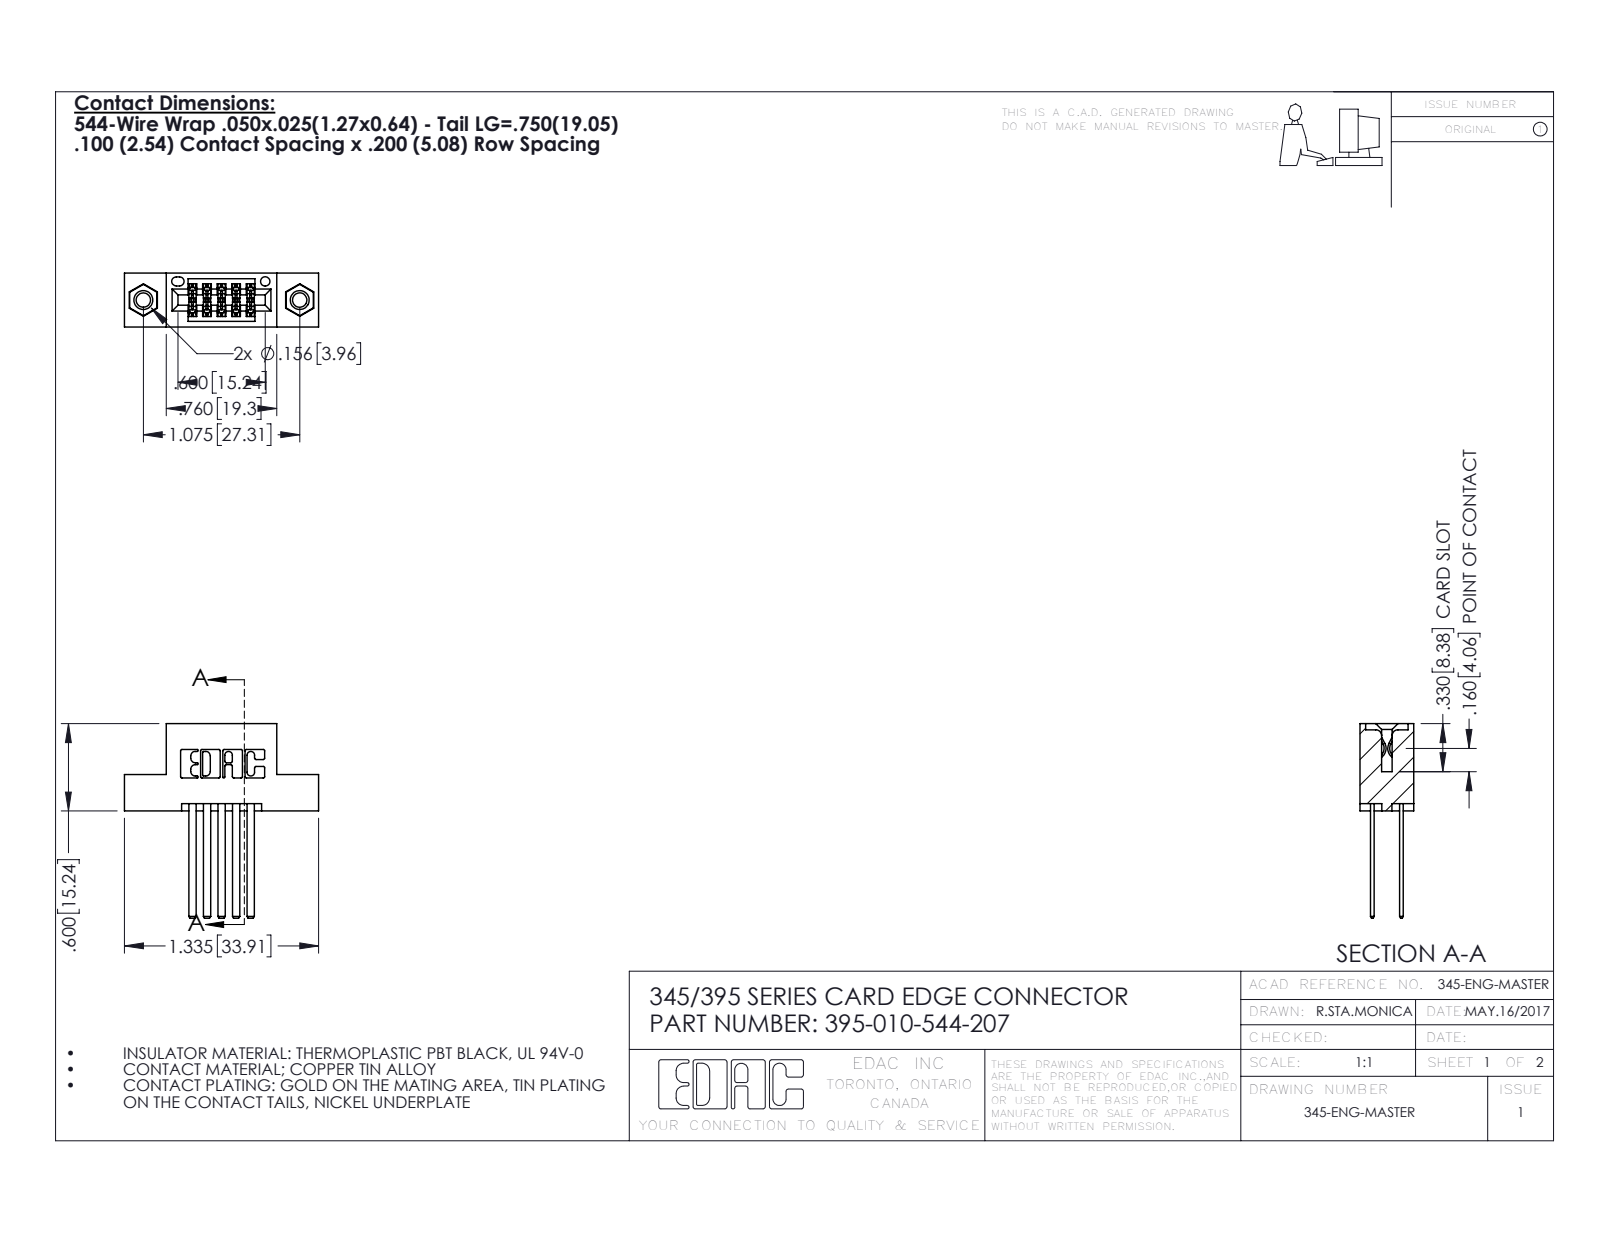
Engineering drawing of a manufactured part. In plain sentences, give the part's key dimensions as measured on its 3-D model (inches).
The part is named "345-250-001_345-250-005-103; 345-292-001_345-293-144; 395-010-544-207; 345 Part_Flush Mounting Lugs - 0.156 Dia-TI". Its 3-D file was written by "SolidWorks 2016 (CONFIG_CONTROL_DESIGN)". It is 13 solids with 626 faces: 402 planar, 208 cylindrical and 16 other. Overall it measures 1.337 by 1.335 by 0.37 inches. Its volume is 0.188 cubic inches and its surface area 6.62 square inches. Round holes: 2 of diameter 0.098, 2 of diameter 0.125, 2 of diameter 0.156, 1 of diameter 0.064. Round bosses or shafts: 2 of diameter 0.155. Partial cylindrical surfaces (rounded edges, fillets, slot ends): 22 of radius 0.01, 15 of radius 0.006, 6 of radius 0.007, 6 of radius 0.031, 3 of radius 0.026, 2 of radius 0.014, 2 of radius 0.019, 2 of radius 0.022. The main face-to-face distances are 0.2, 0.072, 0.298, 0.05, 0.098, 0.272, 0.025, 0.15, 0.1, 0.37. The hole center spacings are 0.27, 0.847, 1.075.
